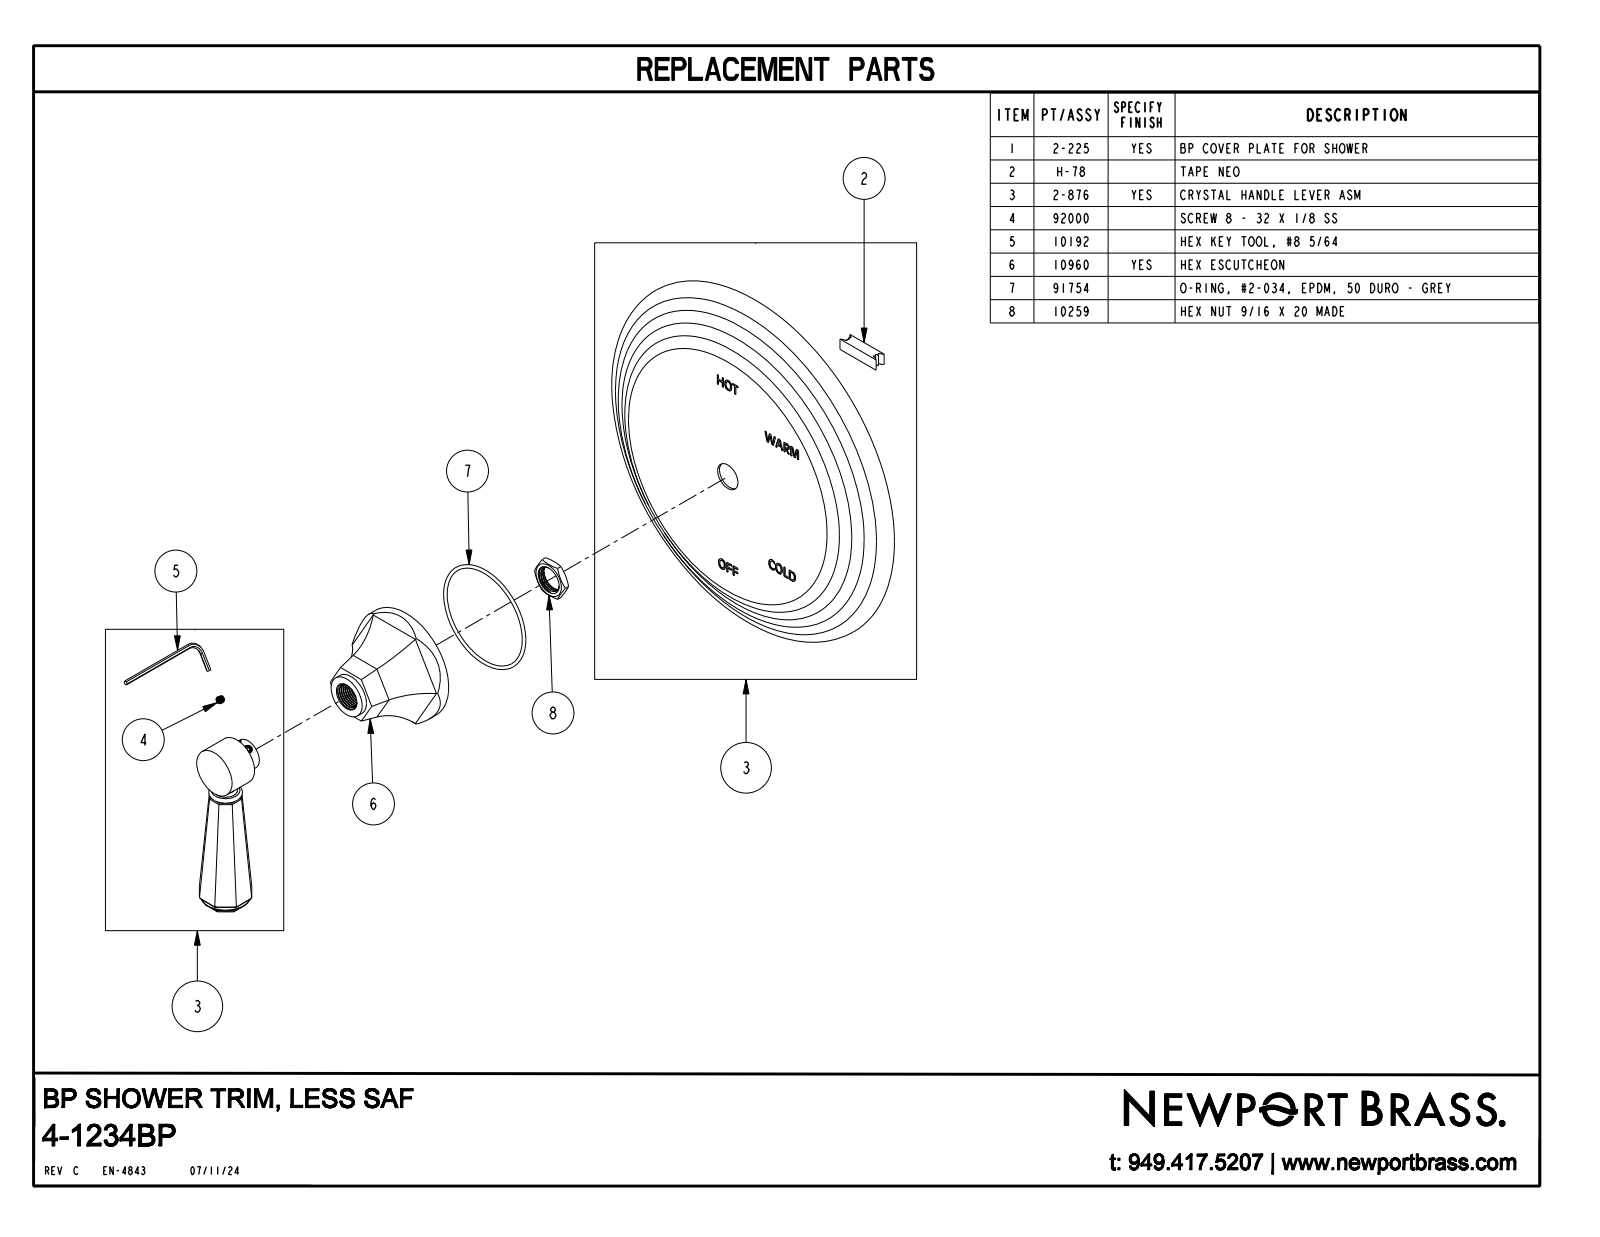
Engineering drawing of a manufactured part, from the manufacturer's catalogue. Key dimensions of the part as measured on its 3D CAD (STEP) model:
Part name (STEP PRODUCT): 4-1234BP
STEP written by: CREO PARAMETRIC BY PTC INC, 2018400 (CONFIG_CONTROL_DESIGN)
Units: inches
Bodies: 1 solid, 350 faces (192 planar, 46 cylindrical, 112 other)
Overall size (bounding box): 7.75 × 7.75 × 3.557
Volume: 33.25 in³ · Surface area: 119.7 in²
Round holes (diameter × count): ⌀0.385 ×1
Round bosses / shafts (diameter × count): ⌀0.98 ×2, ⌀2.375 ×1, ⌀0.86 ×1, ⌀0.625 ×1, ⌀0.4 ×1, ⌀0.365 ×1
Partial cylindrical surfaces — rounded edges, fillets, slot ends (radius × count): R0.03 ×24, R1.541 ×6
Main face-to-face distances: 0.754, 2.401, 1.647, 2.731, 1.977, 0.33, 2.281, 1.527, 0.12, 0.45
